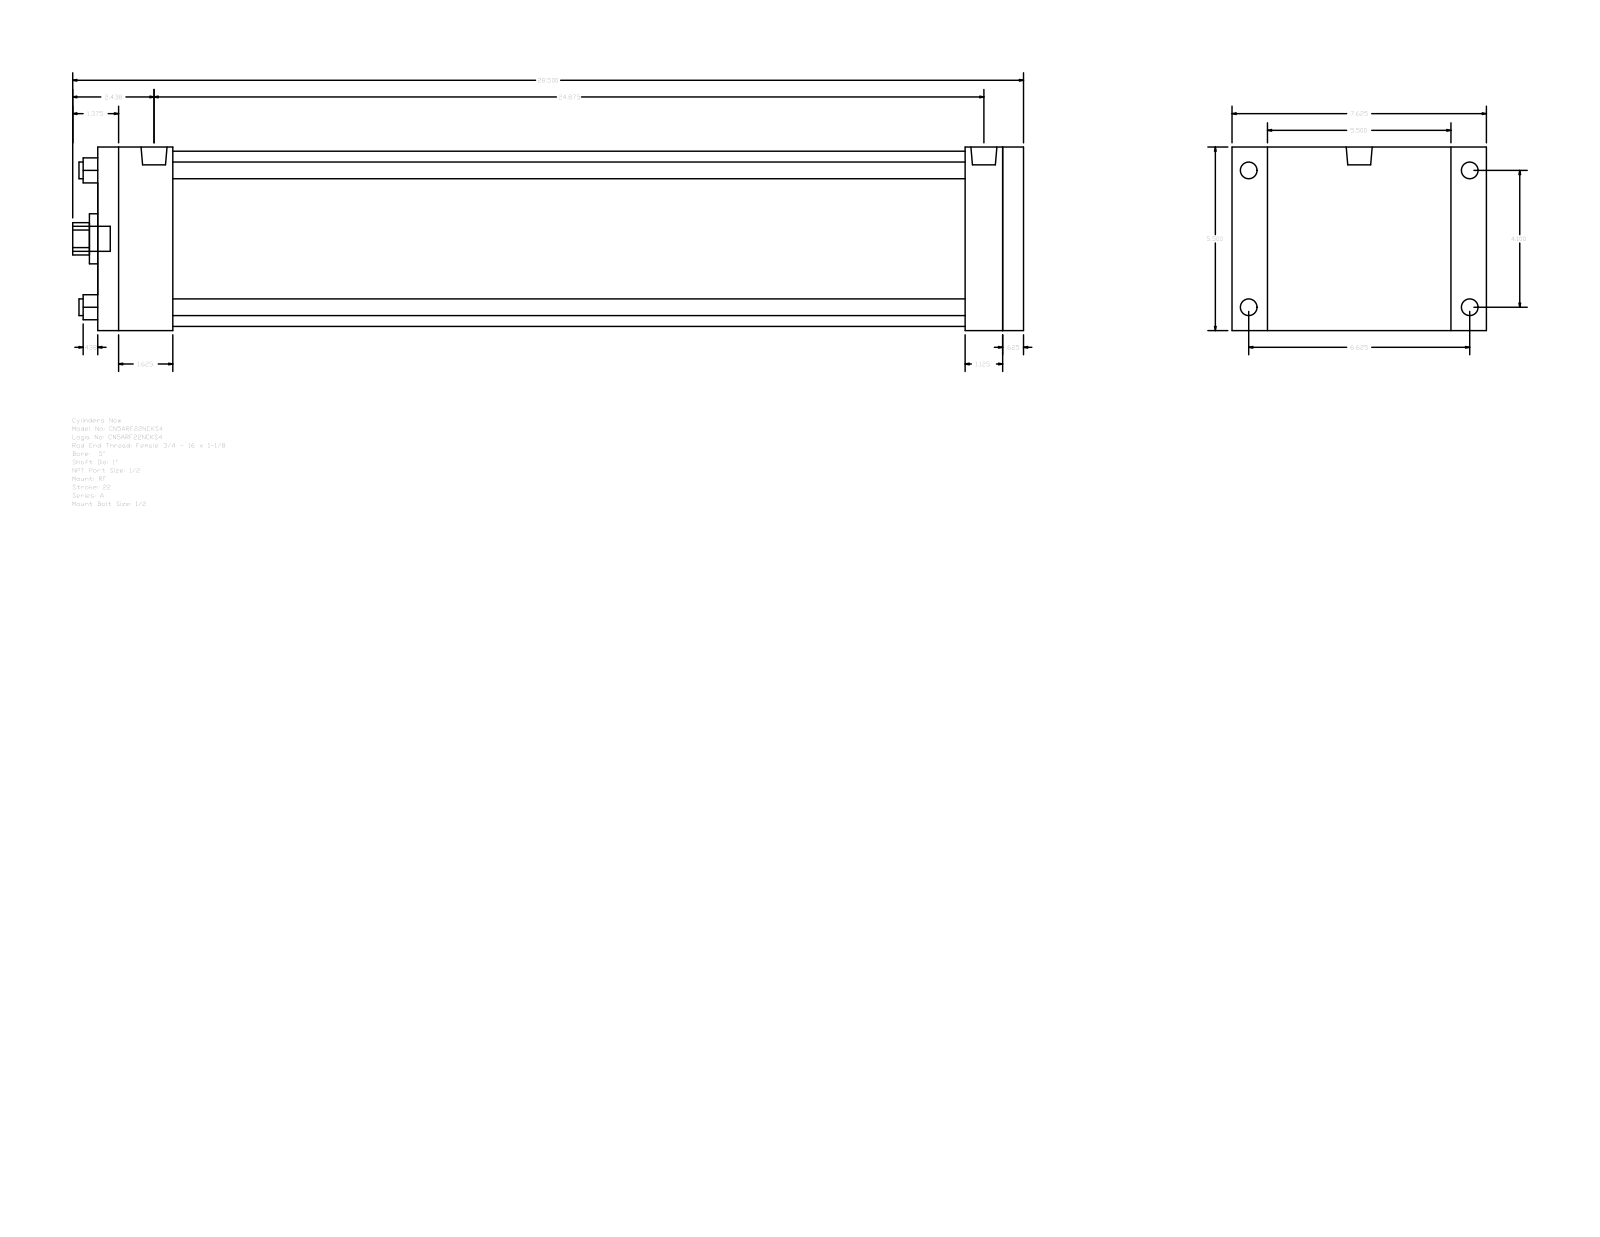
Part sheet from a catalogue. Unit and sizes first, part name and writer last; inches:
Units: inches
Overall size (bounding box): 28.5 × 7.625 × 5.5
Round holes (diameter × count): ⌀0.5 ×4, ⌀1 ×1, ⌀1.5 ×1, ⌀5.25 ×1
Round bosses / shafts (diameter × count): ⌀0.5 ×4, ⌀0.344 ×4, ⌀0.778 ×2, ⌀0.75 ×1
Partial cylindrical surfaces — rounded edges, fillets, slot ends (radius × count): R0.484 ×1
Main face-to-face distances: 5.5, 27.75, 27.125, 0.625, 1.125, 2.25, 24.875, 25.5, 26, 23.75
Hole centre spacings: 2.899, 4.1, 5.798
Bodies: 0 solids, 92 faces (64 planar, 28 cylindrical, 0 other)
Part name (STEP PRODUCT): A_RF__0500_1
STEP written by: GSSL Pune (CONFIG_CONTROL_DESIGN)
